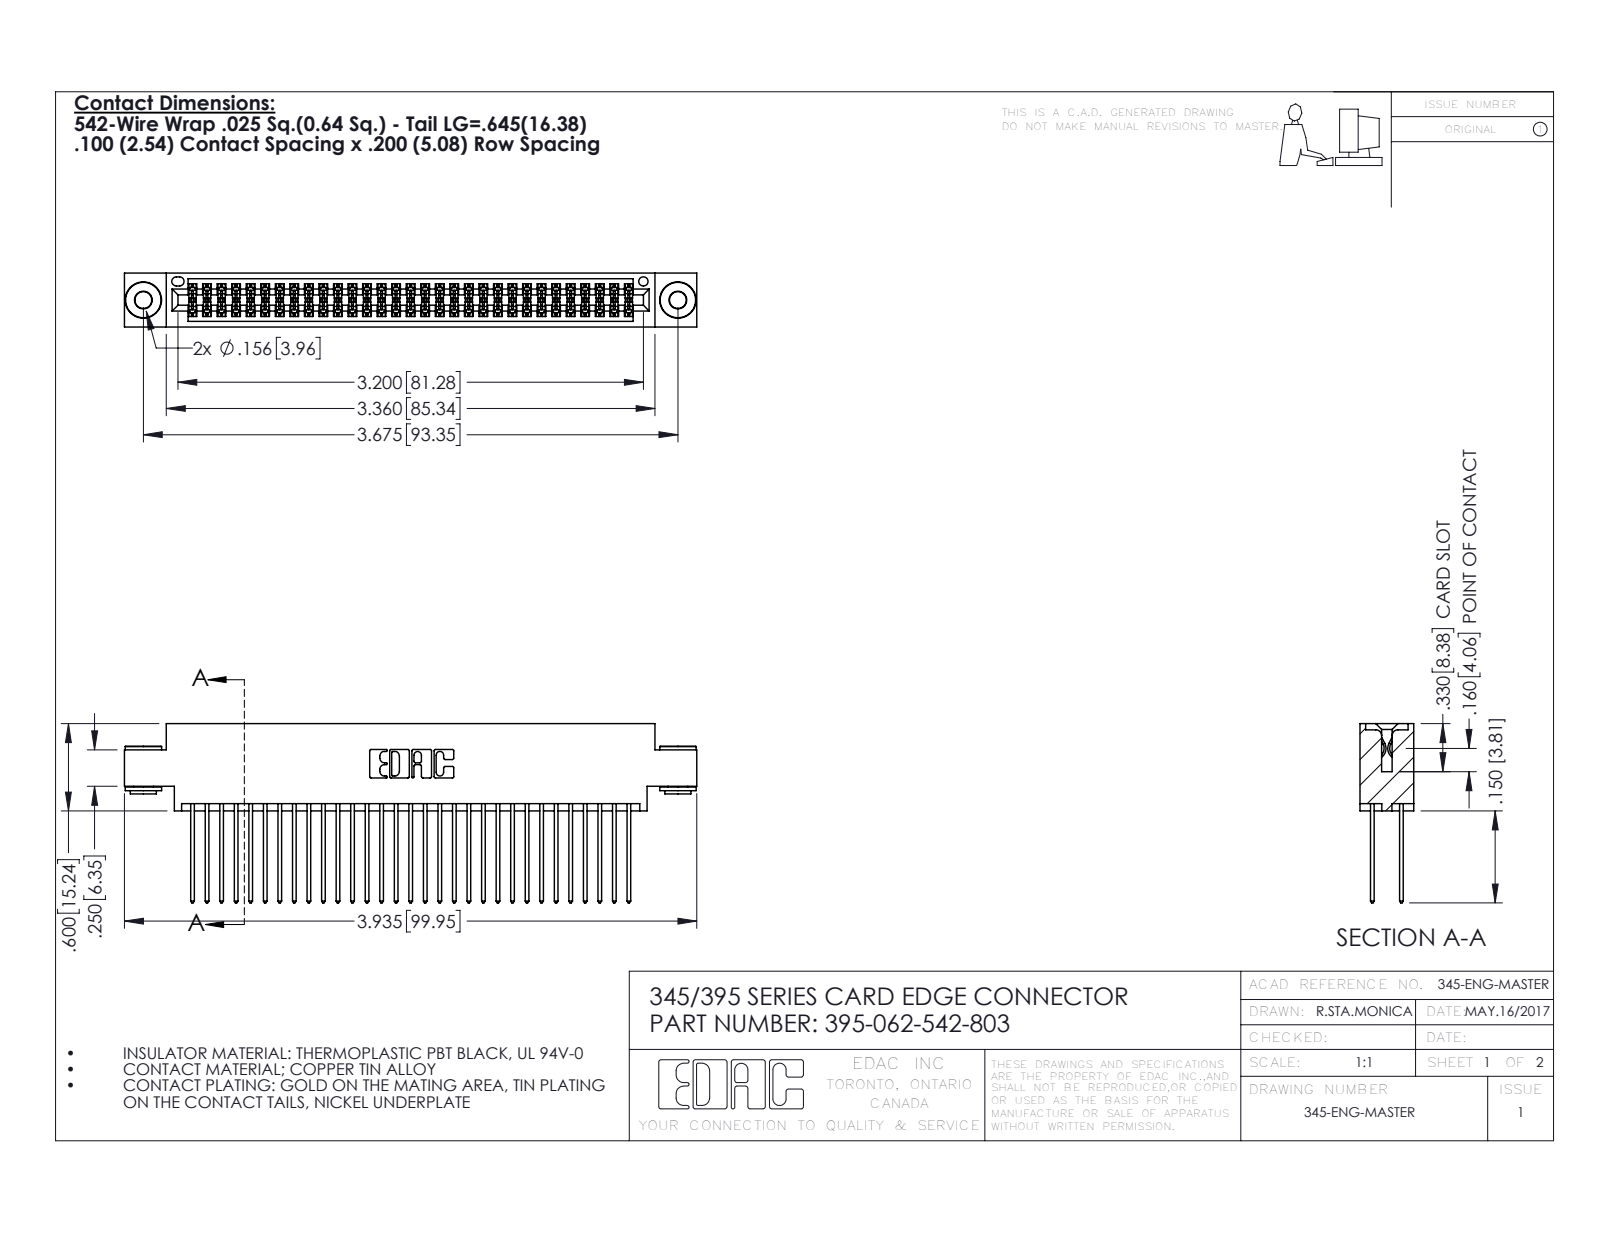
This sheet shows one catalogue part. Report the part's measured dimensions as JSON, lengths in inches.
{"part_name": "395-062-542-803; 345-292-001_345-293-142; 345 Part_0.170 Offset - 0.156 Dia-TH; 345-250-002_345-250-002-102", "step_written_by": "SolidWorks 2016 (CONFIG_CONTROL_DESIGN)", "units": "inches", "bodies": {"solids": 65, "faces": 3268, "planar": 2140, "cylindrical": 1120, "other": 8}, "overall_size": [3.935, 1.232, 0.37], "volume_in3": 0.598, "surface_area_in2": 24.76, "round_holes": [[0.116, 2], [0.156, 2], [0.064, 1]], "round_bosses_or_shafts": [[0.25, 2], [0.18, 2], [0.136, 2]], "partial_cylinders_radius": [[0.006, 93], [0.01, 62], [0.01, 22], [0.007, 6], [0.031, 6], [0.026, 3], [0.014, 2], [0.019, 2]], "face_to_face_distances": [0.072, 0.298, 0.2, 0.098, 0.272, 0.025, 0.37, 0.225, 0.175, 0.149], "hole_center_spacings": [0.27, 3.44, 3.675]}
